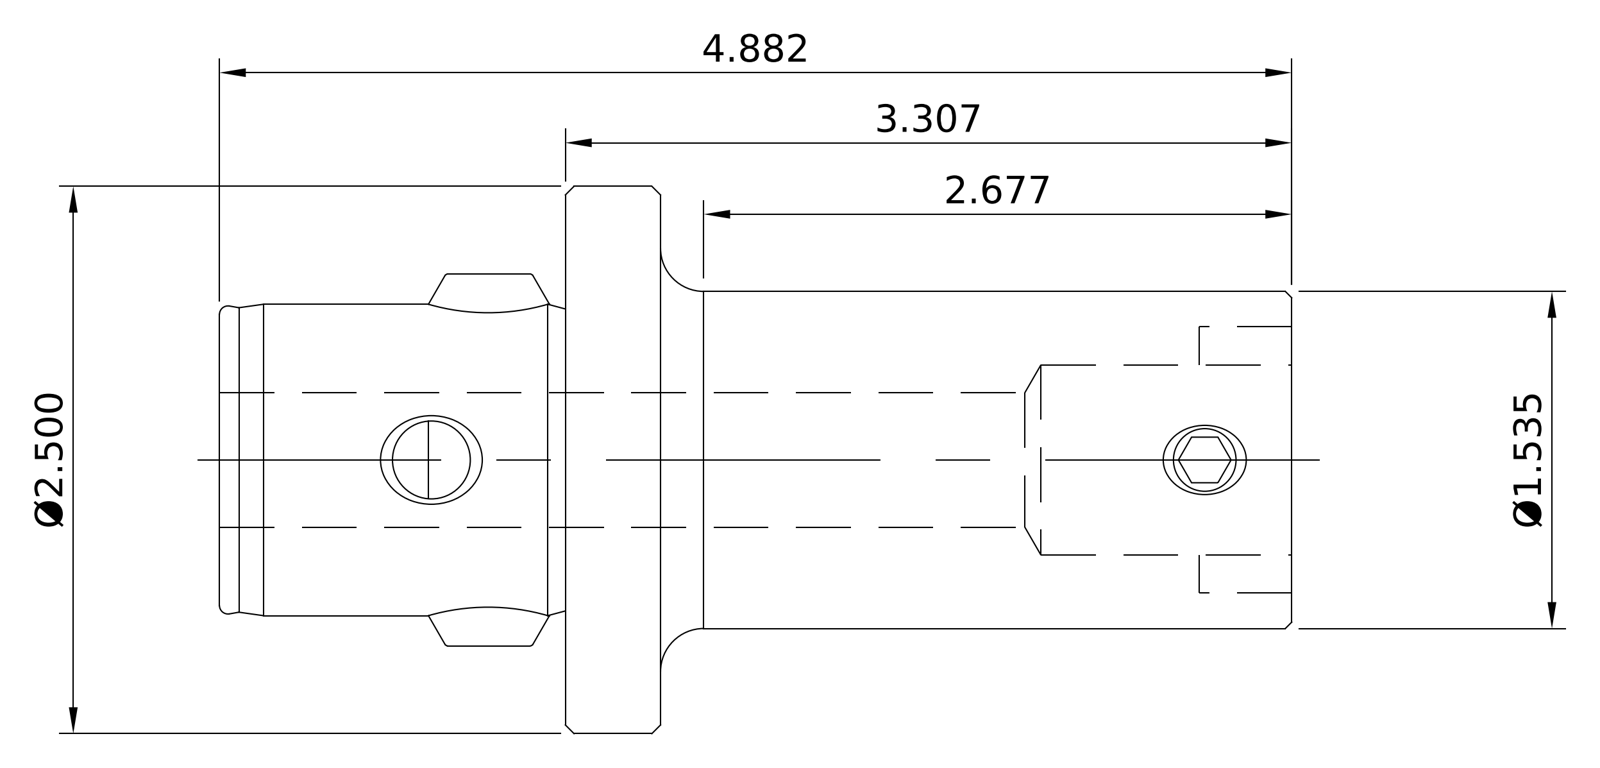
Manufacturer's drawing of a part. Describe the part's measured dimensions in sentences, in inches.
The part is named "691-50XRing_10.691.506Ring; 10.691.50X_10.691.506; 10.690.43X_10.690.434; 11.332.640_10.332.640 (+1 more)". Its 3-D file was written by "SolidWorks 2014 (AUTOMOTIVE_DESIGN)". It is 4 solids with 149 faces: 42 planar, 51 cylindrical and 56 other. Overall it measures 4.882 by 2.491 by 2.491 inches. Its volume is 8.225 cubic inches and its surface area 49.04 square inches. Round holes: 1 of diameter 0.197, 1 of diameter 0.268, 1 of diameter 0.323, 1 of diameter 0.354, 1 of diameter 0.551, 1 of diameter 0.63, 1 of diameter 0.65, 1 of diameter 0.728, 1 of diameter 0.866, 1 of diameter 0.886. Round bosses or shafts: 1 of diameter 2.491, 1 of diameter 1.535, 1 of diameter 1.52, 1 of diameter 1.417, 1 of diameter 0.547, 1 of diameter 0.469, 1 of diameter 0.39, 1 of diameter 0.315. Partial cylindrical surfaces (rounded edges, fillets, slot ends): 2 of radius 0.138, 1 of radius 0.709. The main face-to-face distances are 0.472, 1.575, 2.047, 4.882, 3.307, 2.835, 1.693, 3.74, 2.165, 1.142. The hole center spacings are 0.591, 3.522.
